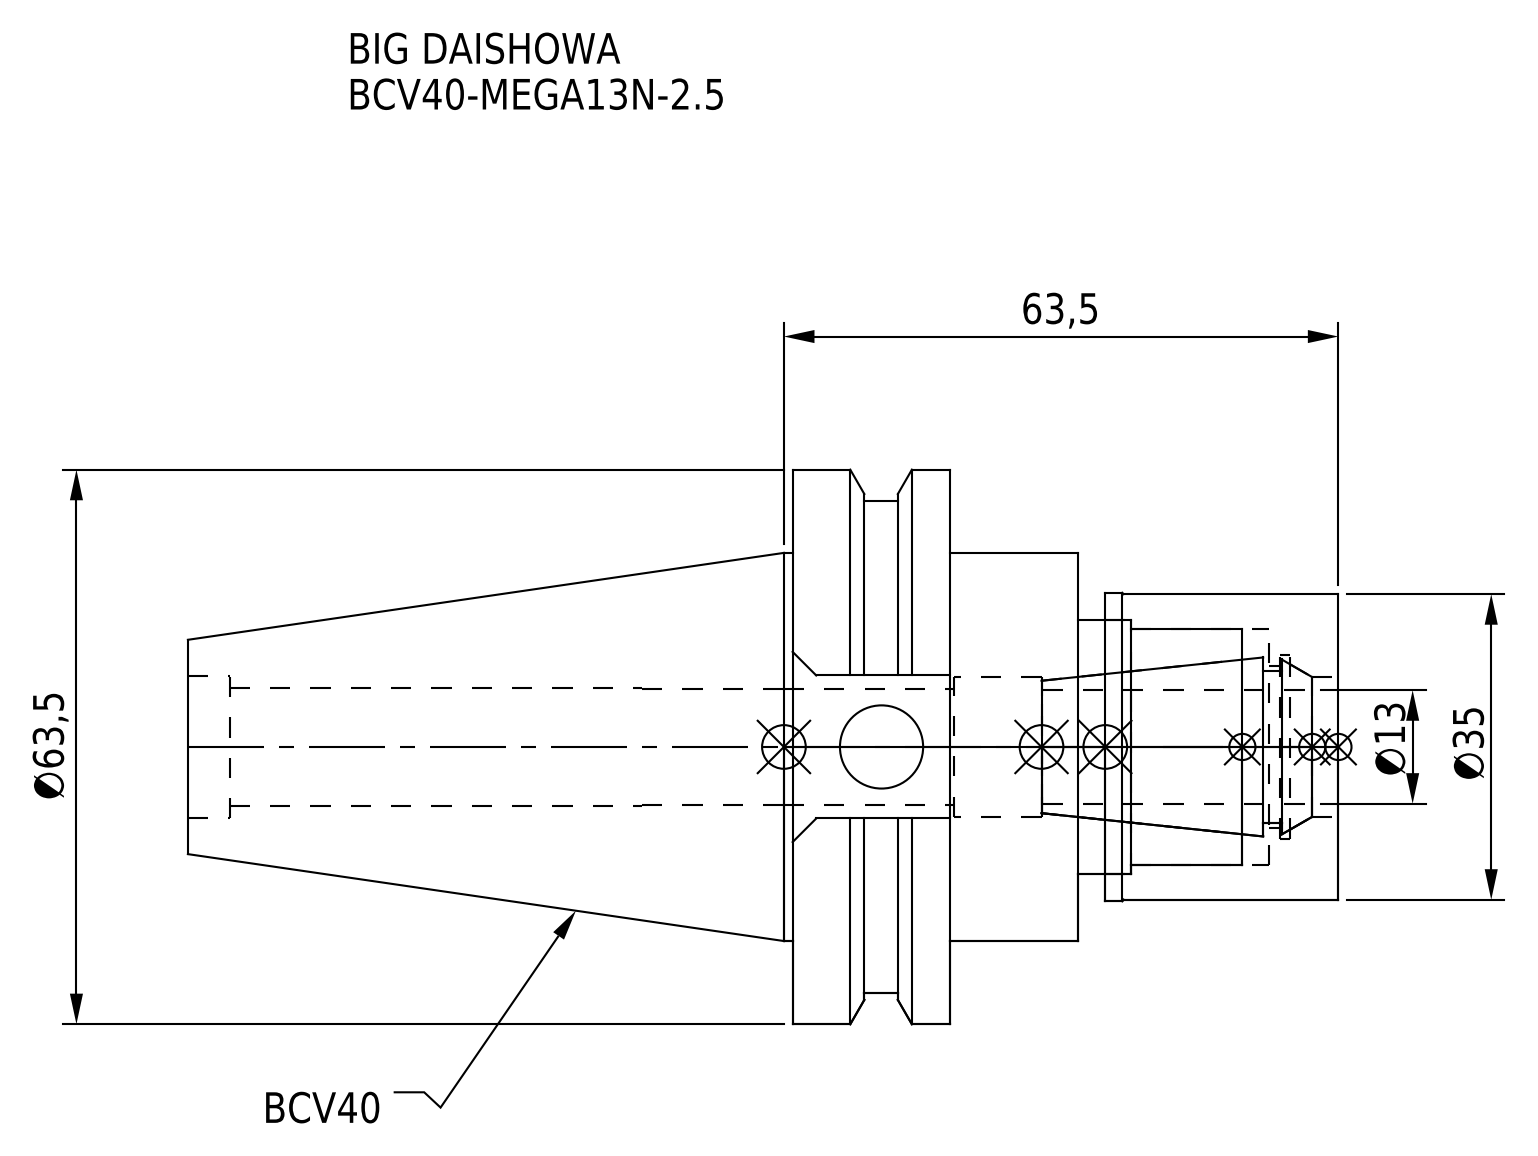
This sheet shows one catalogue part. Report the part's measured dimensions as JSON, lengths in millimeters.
{"part_name": "MGN13_1.stp; BCV40MN13025-130_ASM.stp; BCV40-MEGA13N-2_5_1.stp; BCV40-MEGA13N-2_5-130-FreeParts (+3 more)", "step_written_by": "SolidWorks 2019 (CONFIG_CONTROL_DESIGN)", "units": "millimeters", "bodies": {"solids": 2, "faces": 83, "planar": 31, "cylindrical": 40, "other": 12}, "overall_size": [131.75, 63.5, 61.35], "volume_mm3": 143164, "surface_area_mm2": 32446, "round_holes": [[9.53, 1], [13.3, 1], [13.6, 1], [16, 1], [16.32, 1], [18.5, 1], [21, 1], [27, 1], [29, 1]], "round_bosses_or_shafts": [[63.5, 1], [56.36, 1], [44.45, 1], [35.3, 1], [35, 1]], "face_to_face_distances": [18.05, 14.65, 32.7, 29.8, 44.45, 62.5, 26.7, 3.1, 17.75, 35.8]}
